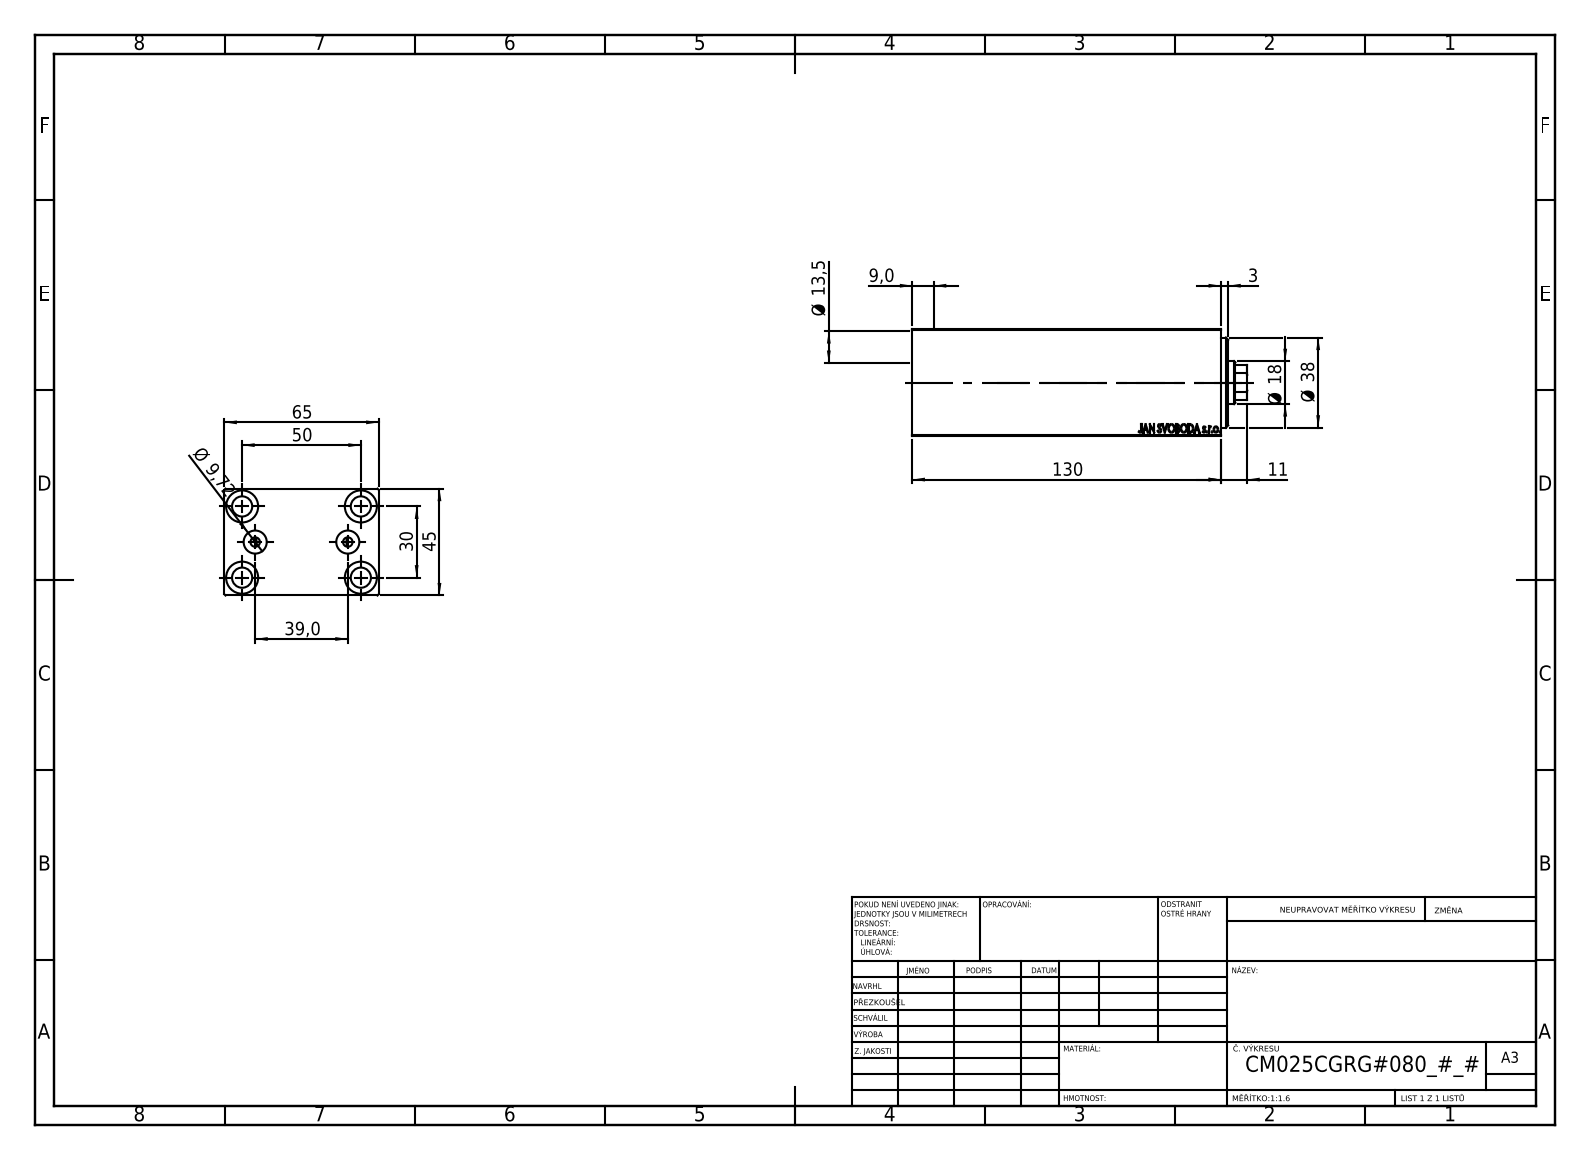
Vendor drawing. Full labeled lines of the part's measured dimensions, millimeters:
Part name (STEP PRODUCT): V450CM_C_VCP; V450CM_C_Body; V450CM_VC_B
STEP written by: SolidWorks 2019 (CONFIG_CONTROL_DESIGN)
Units: millimetres
Bodies: 3 solids, 858 faces (408 planar, 56 cylindrical, 394 other)
Overall size (bounding box): 141 × 65 × 45
Volume: 325 150 mm³ · Surface area: 76 071 mm²
Round holes (diameter × count): ⌀8.5 ×5, ⌀13.5 ×4, ⌀4 ×2, ⌀9.72 ×2, ⌀18 ×1, ⌀21.5 ×1, ⌀25 ×1, ⌀27 ×1, ⌀38 ×1
Partial cylindrical surfaces — rounded edges, fillets, slot ends (radius × count): R8.5 ×1
Main face-to-face distances: 45, 65, 6, 119, 124, 125, 5, 130, 3, 8
Hole centre spacings: 15.98, 29.15, 46.96, 19.5, 30, 50, 58.31, 39
